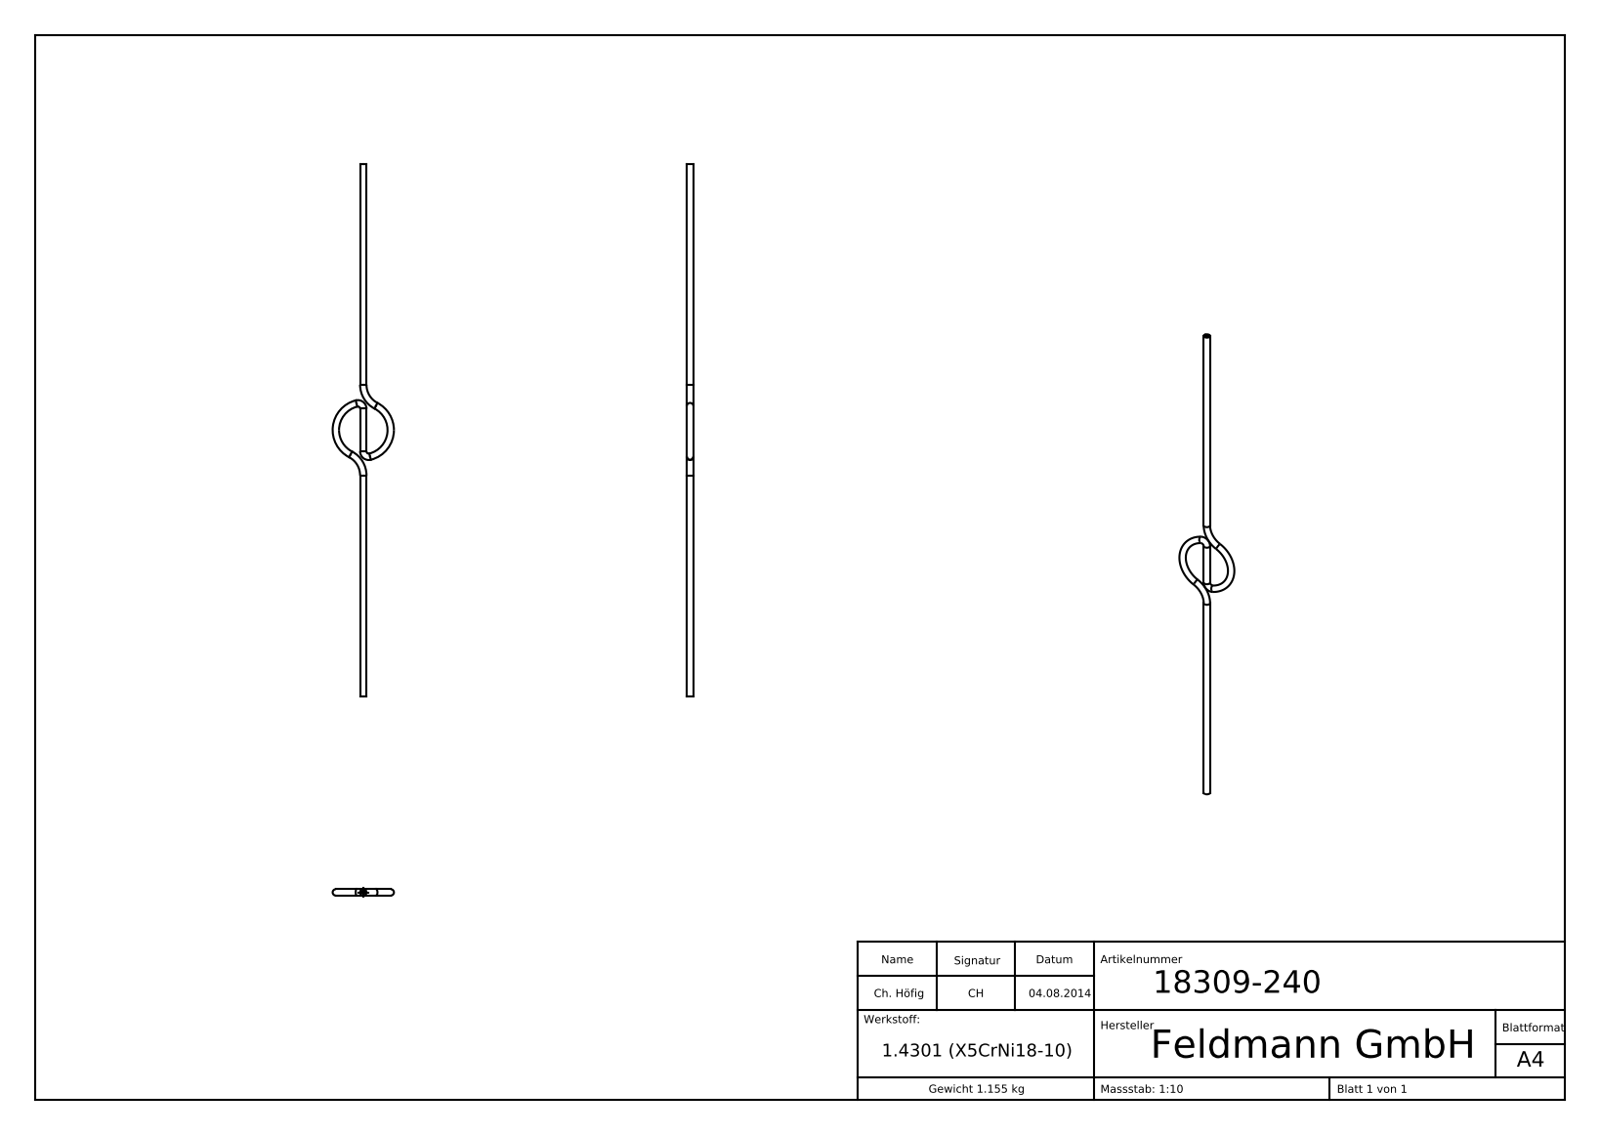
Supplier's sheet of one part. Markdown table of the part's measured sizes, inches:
| quantity | value |
| --- | --- |
| part name | 18309-240 |
| STEP written by | SolidWorks 2015 (CONFIG_CONTROL_DESIGN) |
| units | inches |
| bodies | 1 solid, 137 faces (67 planar, 6 cylindrical, 64 other) |
| overall size | 39.37 × 4.528 × 0.472 |
| volume | 8.918 in³ |
| surface area | 75.89 in² |
| round bosses / shafts (diameter × count) | 0.472 × 1 |
| main face-to-face distances | 39.37, 39.35, 0.02, 0.015, 0.117, 0.044, 0.161, 0.029, 0.05, 0.129 |
